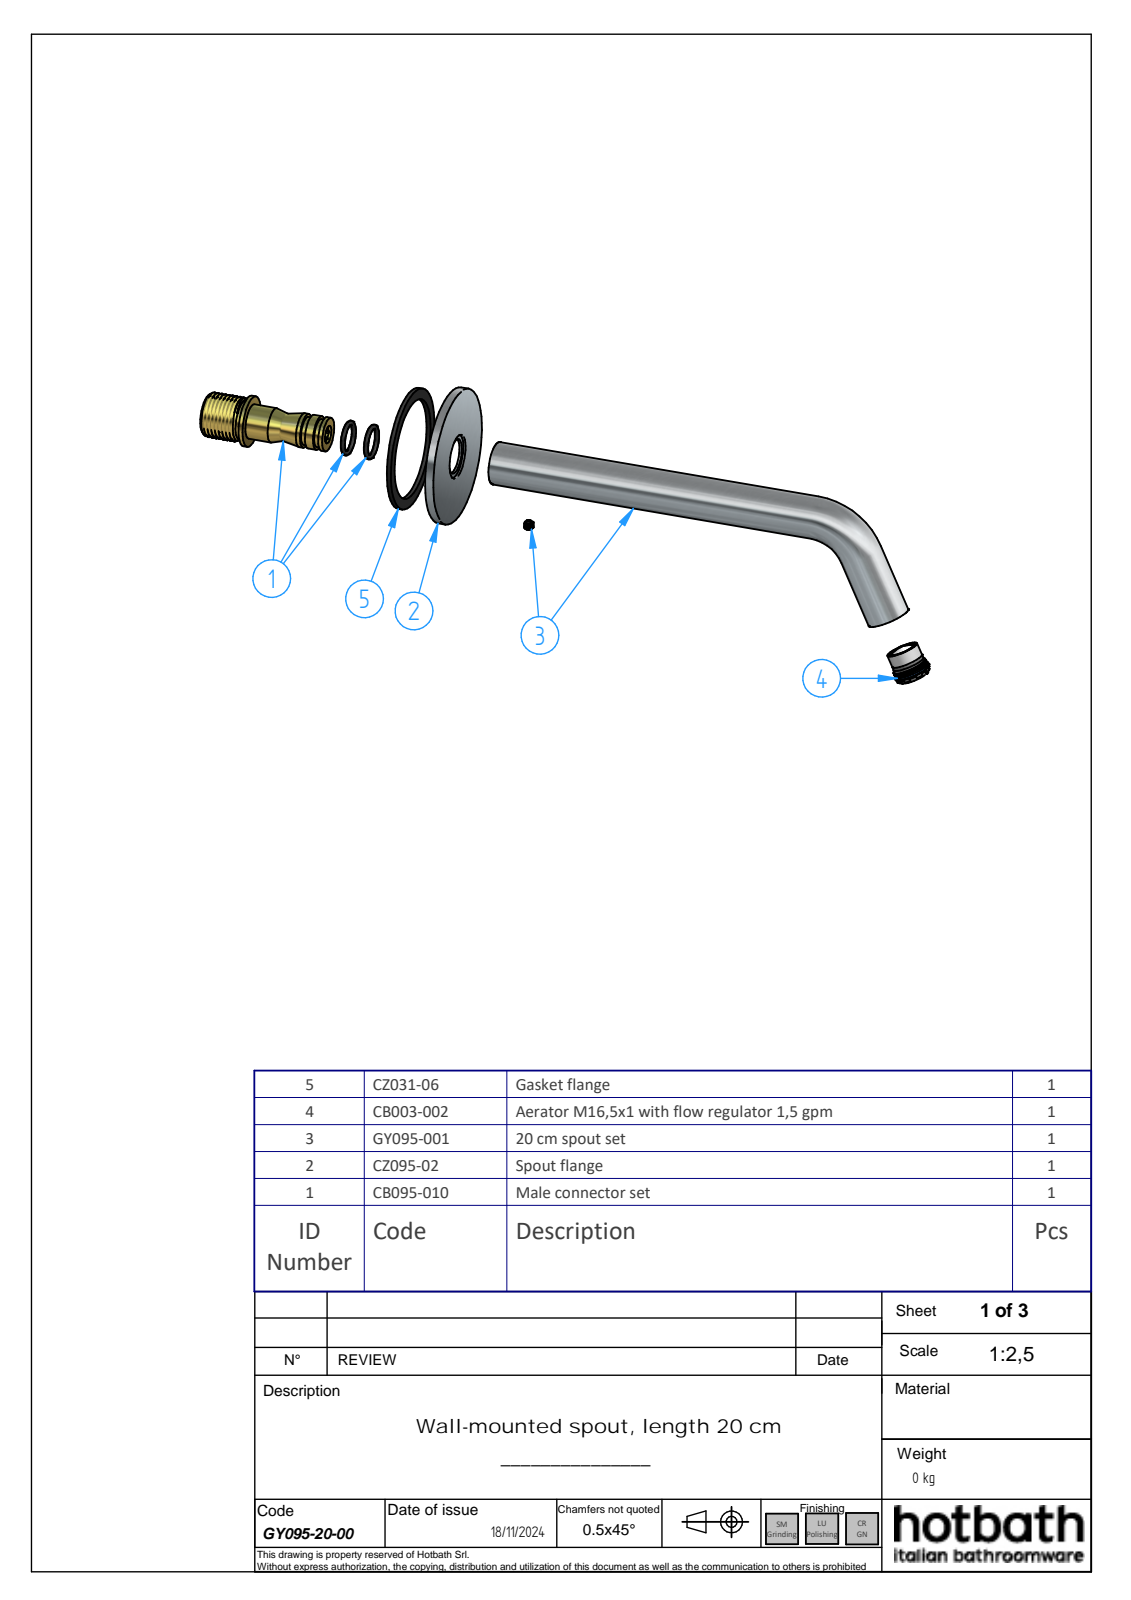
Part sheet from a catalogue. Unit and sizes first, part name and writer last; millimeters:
Units: millimetres
Overall size (bounding box): 207.89 × 80.28 × 64
Round holes (diameter × count): ⌀16 ×2, ⌀3.24 ×1, ⌀4 ×1, ⌀12.2 ×1, ⌀14.58 ×1, ⌀16.1 ×1, ⌀16.3 ×1, ⌀16.5 ×1, ⌀16.75 ×1, ⌀20.5 ×1, ⌀25 ×1, ⌀60.5 ×1
Round bosses / shafts (diameter × count): ⌀20 ×2, ⌀64 ×1, ⌀29 ×1, ⌀16.5 ×1, ⌀15.42 ×1, ⌀15.23 ×1, ⌀15.22 ×1, ⌀15.03 ×1
Main face-to-face distances: 2.3, 2.2, 1, 4, 1.7, 1.8, 0.9, 3, 1.3, 1.2
Volume: 33 616 mm³ · Surface area: 33 717 mm²
Bodies: 4 solids, 136 faces (64 planar, 30 cylindrical, 42 other)
Part name (STEP PRODUCT): GY095-20-00; CZ095-02; GY095-001; GY095-01 (+3 more)
STEP written by: Solid Edge (AUTOMOTIVE_DESIGN)
